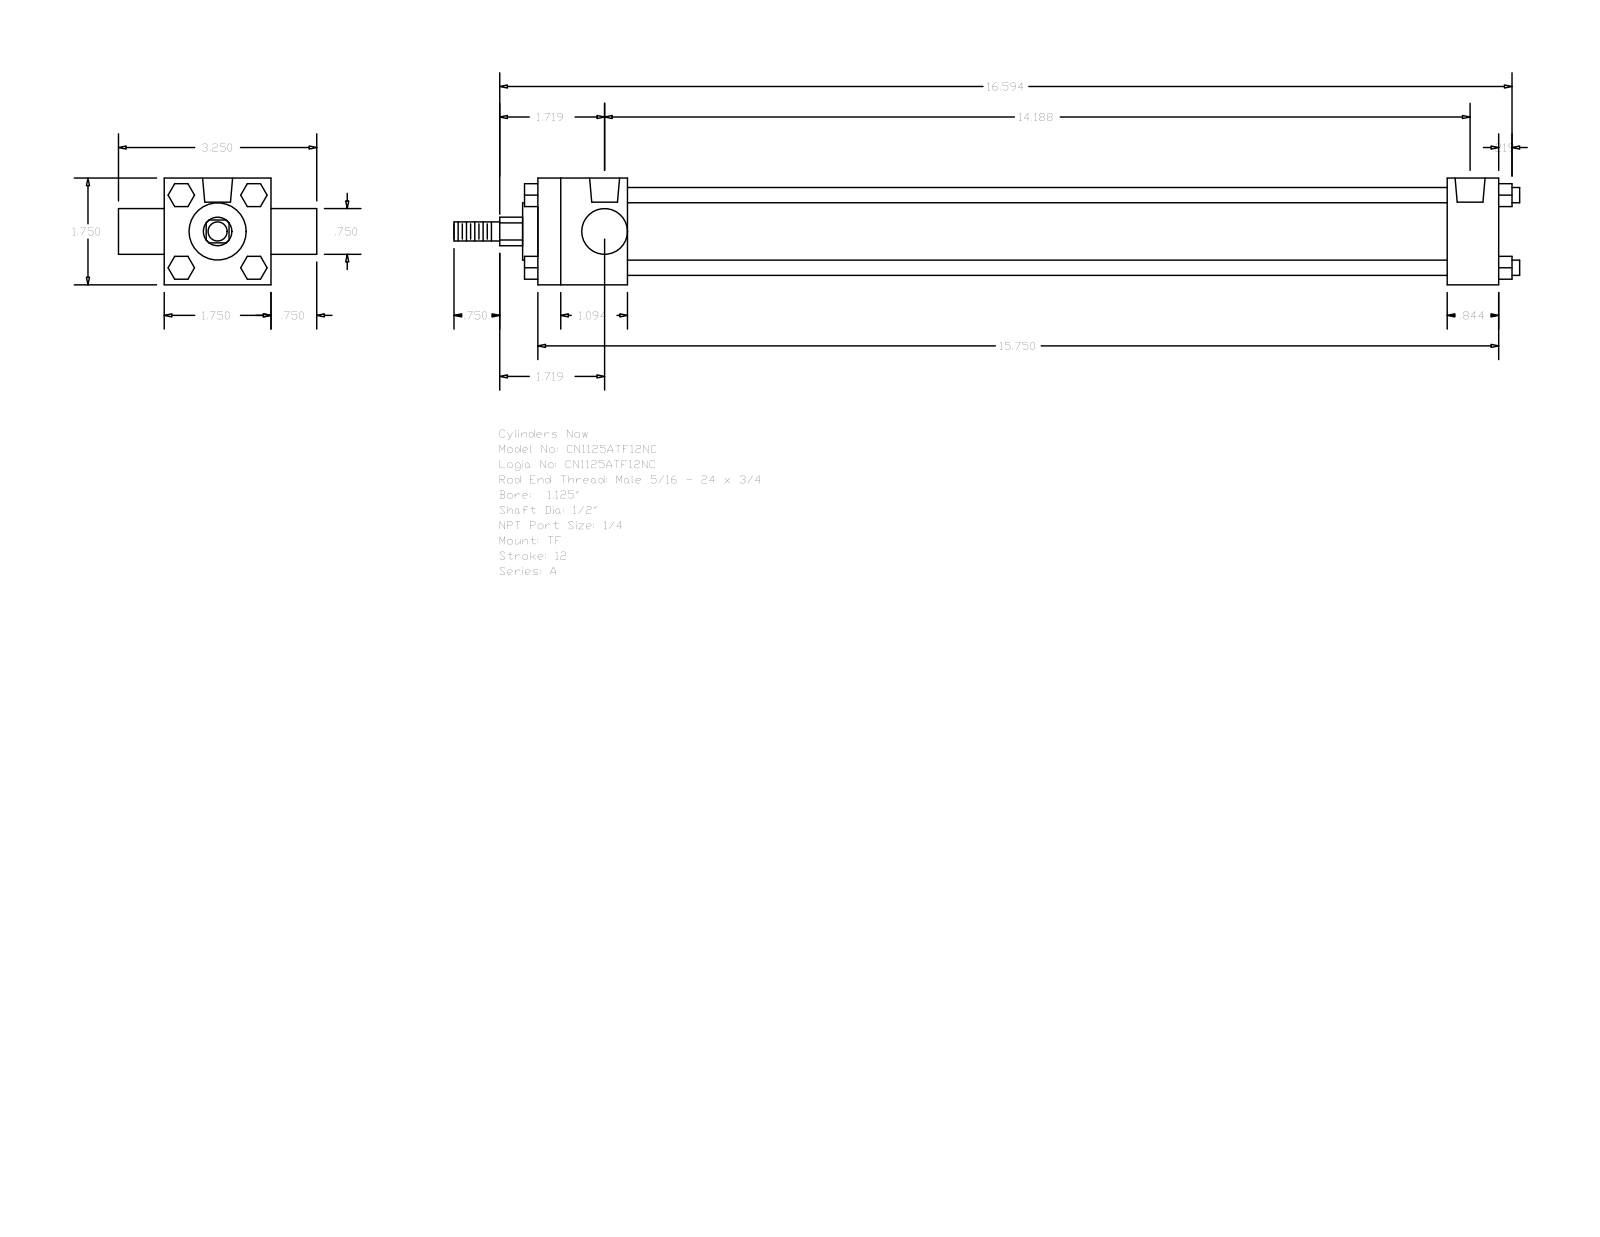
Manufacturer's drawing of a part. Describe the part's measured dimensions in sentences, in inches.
The part is named "A_TF__0112_0.5". Its 3-D file was written by "GSSL Pune (CONFIG_CONTROL_DESIGN)". It is 0 solids with 120 faces: 92 planar, 28 cylindrical and 0 other. Overall it measures 17.469 by 3.25 by 1.75 inches. Round holes: 3 of diameter 0.219, 2 of diameter 0.492. Round bosses or shafts: 4 of diameter 0.25, 1 of diameter 1.255, 1 of diameter 0.937, 1 of diameter 0.75, 1 of diameter 0.5, 1 of diameter 0.313. Partial cylindrical surfaces (rounded edges, fillets, slot ends): 1 of radius 0.234. The main face-to-face distances are 1.75, 15.75, 14.906, 0.844, 1.469, 13.437, 14.281, 0.75, 2.5, 0.375. The hole center spacings are 0.062, 0.063, 14.063, 14.125, 14.125, 14.187.
